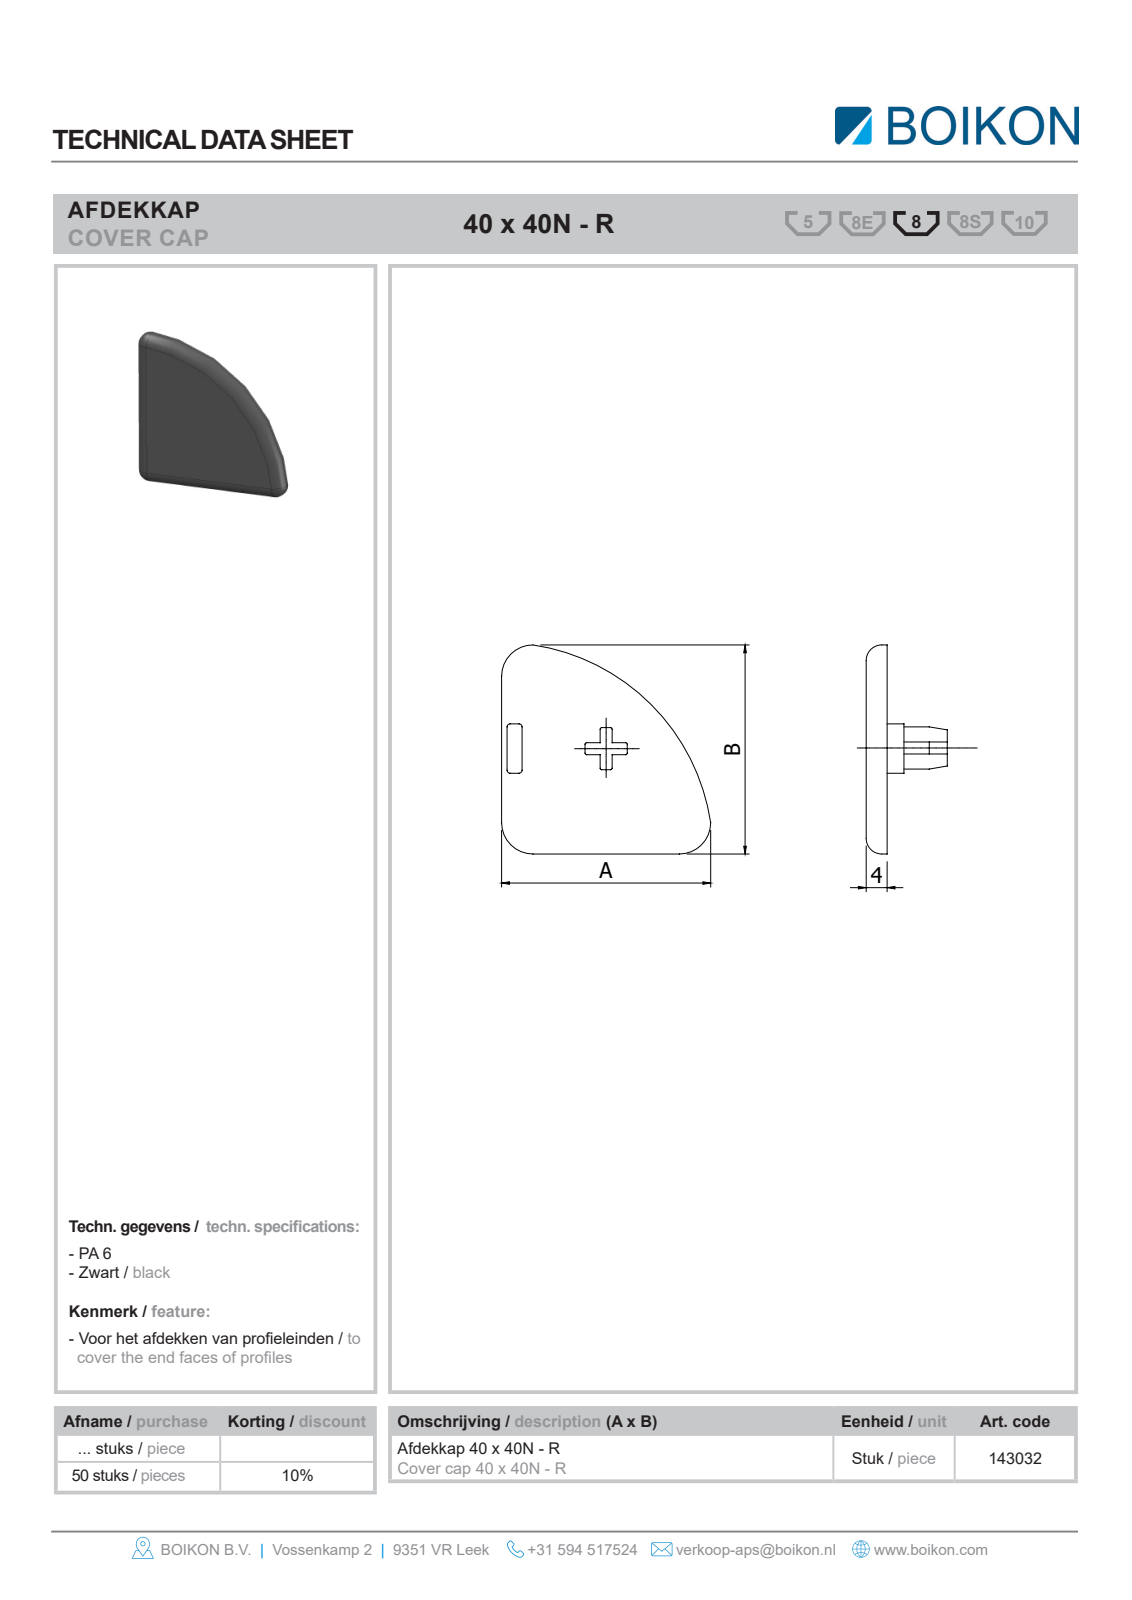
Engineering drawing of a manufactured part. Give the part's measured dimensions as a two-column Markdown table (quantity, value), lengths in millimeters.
| quantity | value |
| --- | --- |
| part name | Root; 143032 Afdekkap 40 x 40 RBOIKON |
| STEP written by | HiCAD 2013 1802.4 Build 509 (AUTOMOTIVE_DESIGN) |
| units | millimeters |
| bodies | 1 solid, 14 faces (4 planar, 6 cylindrical, 4 other) |
| overall size | 39.88 × 39.88 × 4 |
| volume | 4 742 mm³ |
| surface area | 2 873 mm² |
| partial cylindrical surfaces (radius × count) | 3 × 5, 40 × 1 |
| main face-to-face distances | 4 |
